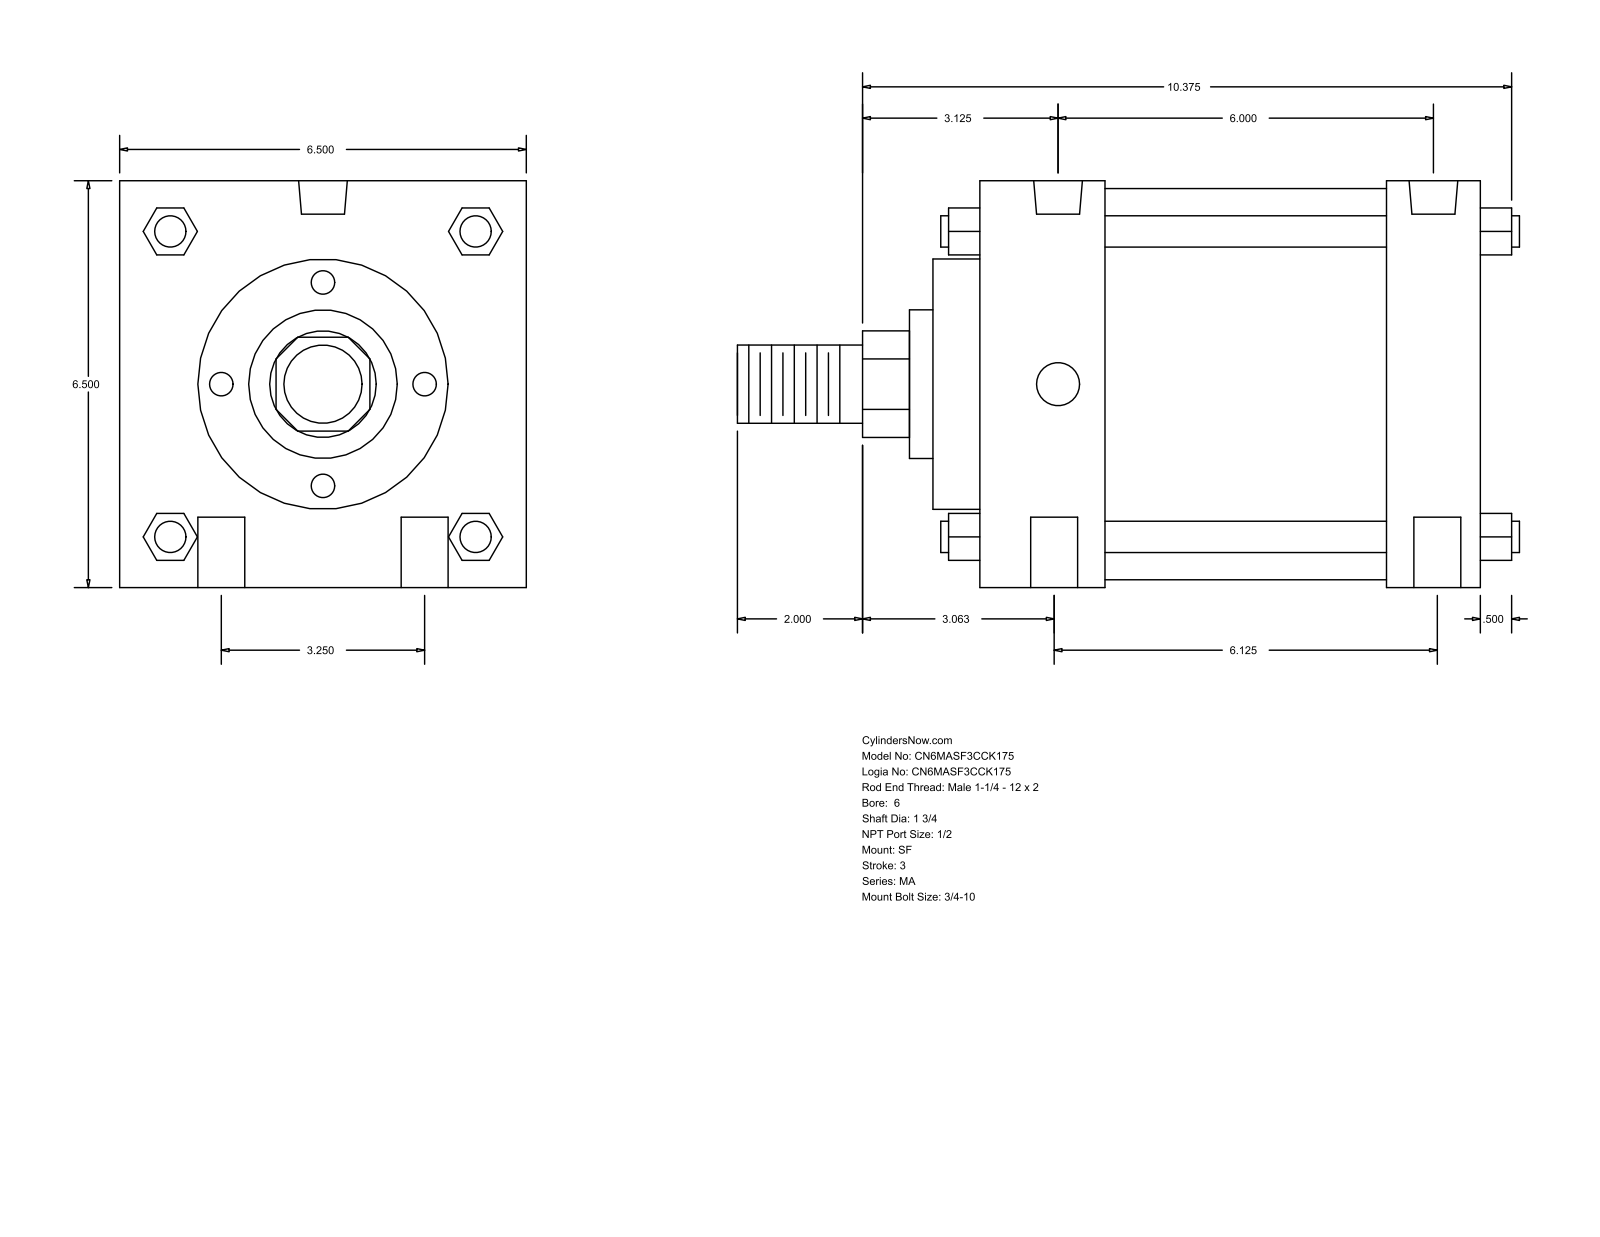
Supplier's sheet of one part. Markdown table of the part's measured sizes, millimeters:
| quantity | value |
| --- | --- |
| part name | MA_SF__0600_1.75 |
| STEP written by | GSSL Pune (CONFIG_CONTROL_DESIGN) |
| units | millimeters |
| bodies | 0 solids, 126 faces (95 planar, 31 cylindrical, 0 other) |
| overall size | 317.5 × 165.1 × 165.1 |
| round holes (diameter × count) | 19.05 × 4, 17.46 × 2, 19.77 × 2 |
| round bosses / shafts (diameter × count) | 12.7 × 4, 158.75 × 1, 101.6 × 1, 60.33 × 1, 44.45 × 1, 31.75 × 1 |
| partial cylindrical surfaces (radius × count) | 21.63 × 1 |
| main face-to-face distances | 165.1, 203.2, 19.05, 50.8, 152.4, 38.1, 114.3, 69.85, 184.15, 222.25 |
| hole center spacings | 41.3, 82.54, 152.4, 155.57, 159.41, 159.42, 176.11 |
